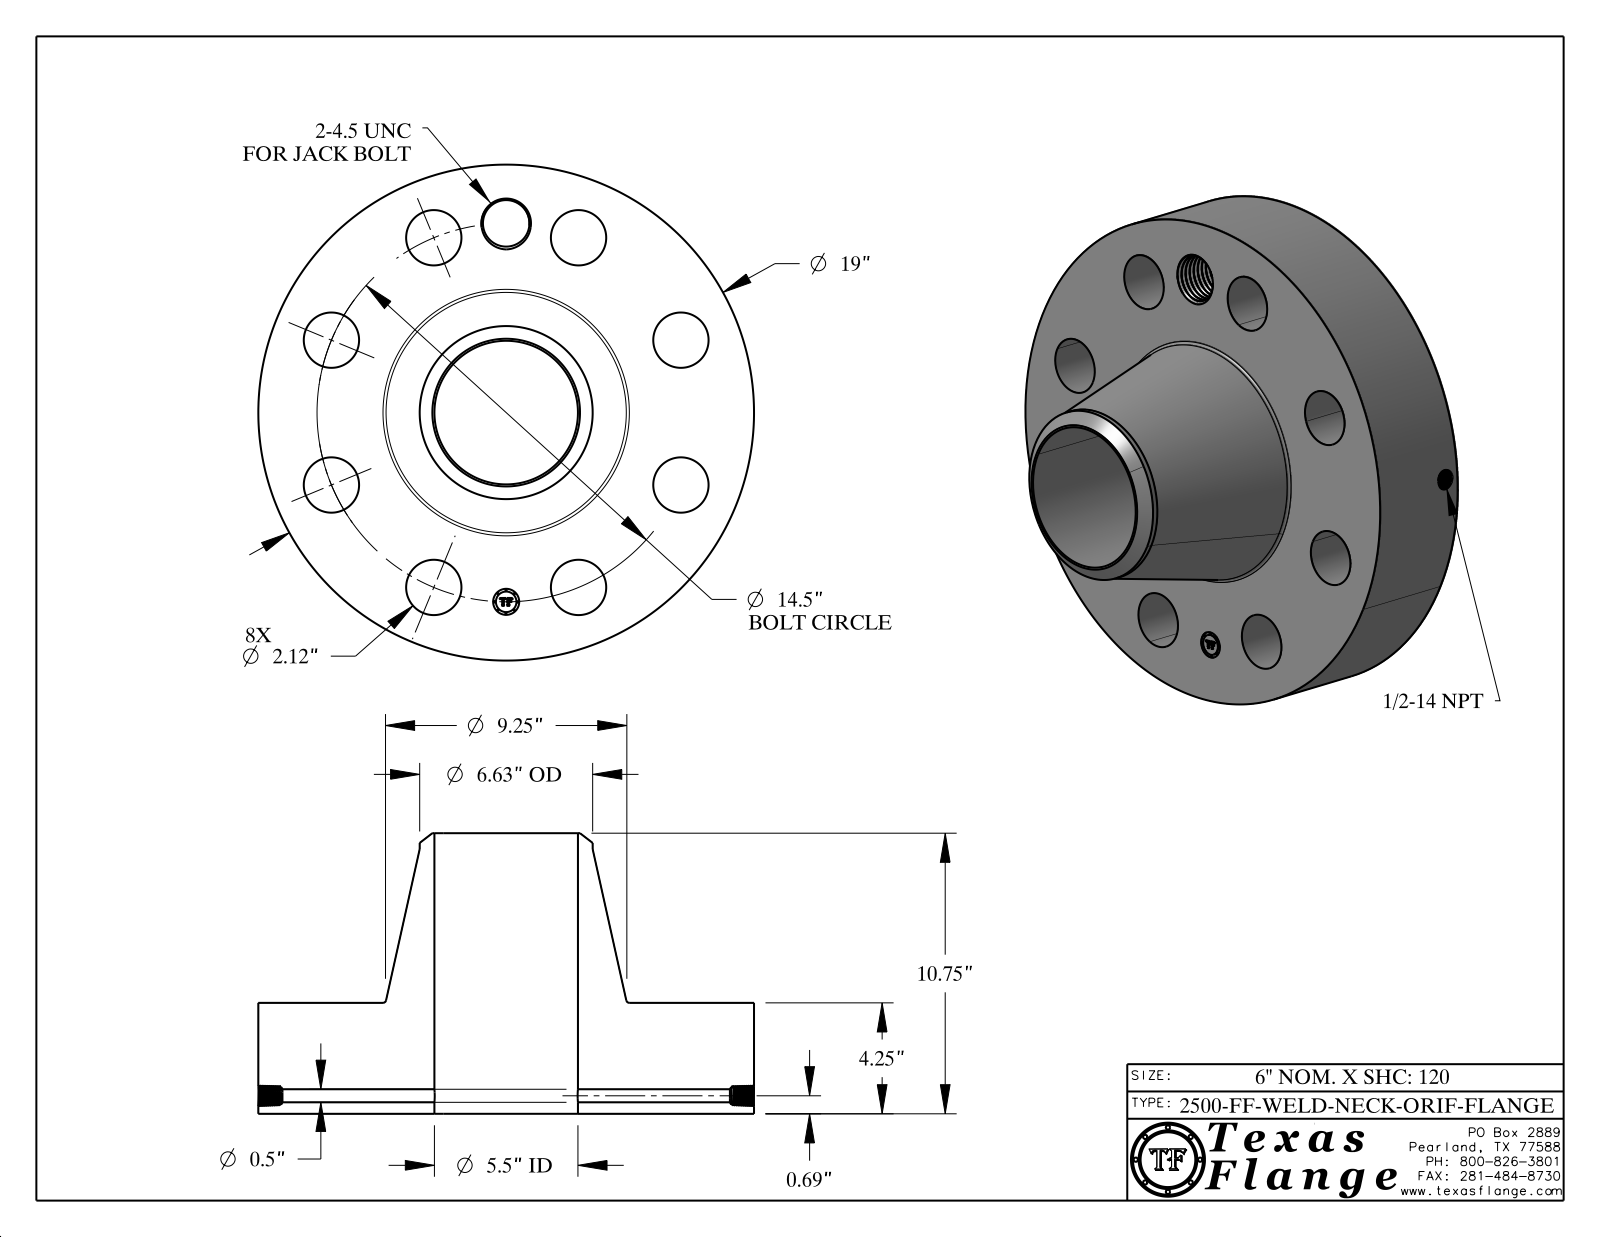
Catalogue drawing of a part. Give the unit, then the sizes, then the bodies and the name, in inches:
Units: inches
Overall size (bounding box): 19 × 19 × 10.75
Round holes (diameter × count): ⌀2.12 ×8, ⌀0.5 ×1, ⌀0.672 ×1, ⌀1 ×1, ⌀1.781 ×1, ⌀5.501 ×1
Round bosses / shafts (diameter × count): ⌀0.061 ×8, ⌀19 ×1, ⌀6.63 ×1, ⌀0.788 ×1
Main face-to-face distances: 4.25, 10.75, 6.5, 4.235, 0.015, 6.515, 0.298, 0.293, 0.054, 0.248
Hole centre spacings: 7.25, 5.549, 10.253, 13.396, 2.829, 8.056, 12.056, 14.221
Volume: 1 128 in³ · Surface area: 1 308 in²
Bodies: 1 solid, 791 faces (368 planar, 100 cylindrical, 323 other)
Part name (STEP PRODUCT): 2500-FF-WELD-NECK
STEP written by: CATIA V5 STEP AP214 (AUTOMOTIVE_DESIGN)
